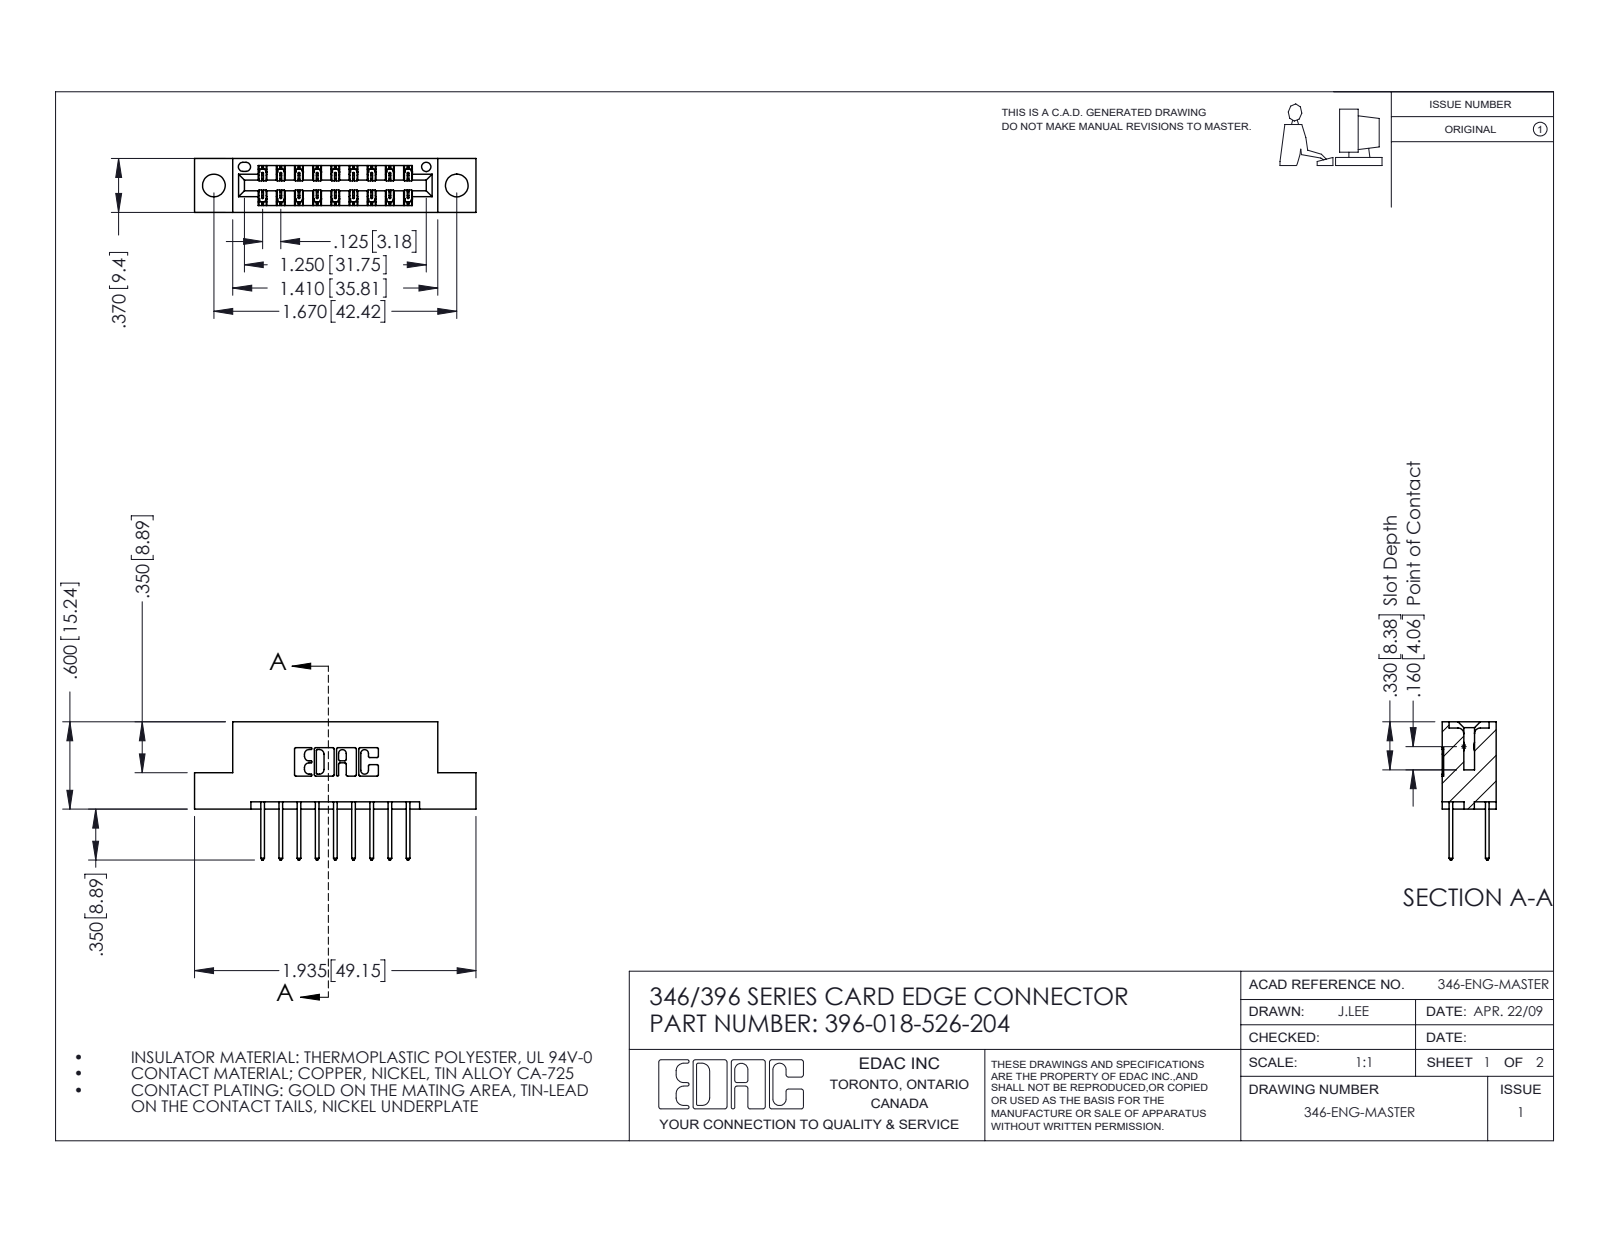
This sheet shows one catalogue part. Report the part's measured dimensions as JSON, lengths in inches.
{"part_name": "396-018-526-204; 346 Part_Flush Mounting Lugs - 0.156 Dia-TH; 345-292-001_345-293-126", "step_written_by": "SolidWorks 2016 (CONFIG_CONTROL_DESIGN)", "units": "inches", "bodies": {"solids": 19, "faces": 1058, "planar": 706, "cylindrical": 352, "other": 0}, "overall_size": [1.935, 0.95, 0.37], "volume_in3": 0.273, "surface_area_in2": 8.652, "round_holes": [[0.156, 2], [0.064, 1]], "partial_cylinders_radius": [[0.006, 27], [0.01, 22], [0.01, 18], [0.007, 6], [0.031, 6], [0.026, 3], [0.014, 2], [0.022, 2]], "face_to_face_distances": [0.25, 0.048, 0.322, 0.37, 0.072, 0.298, 0.025, 0.275, 0.148, 0.222], "hole_center_spacings": [0.246, 1.465, 1.67]}
